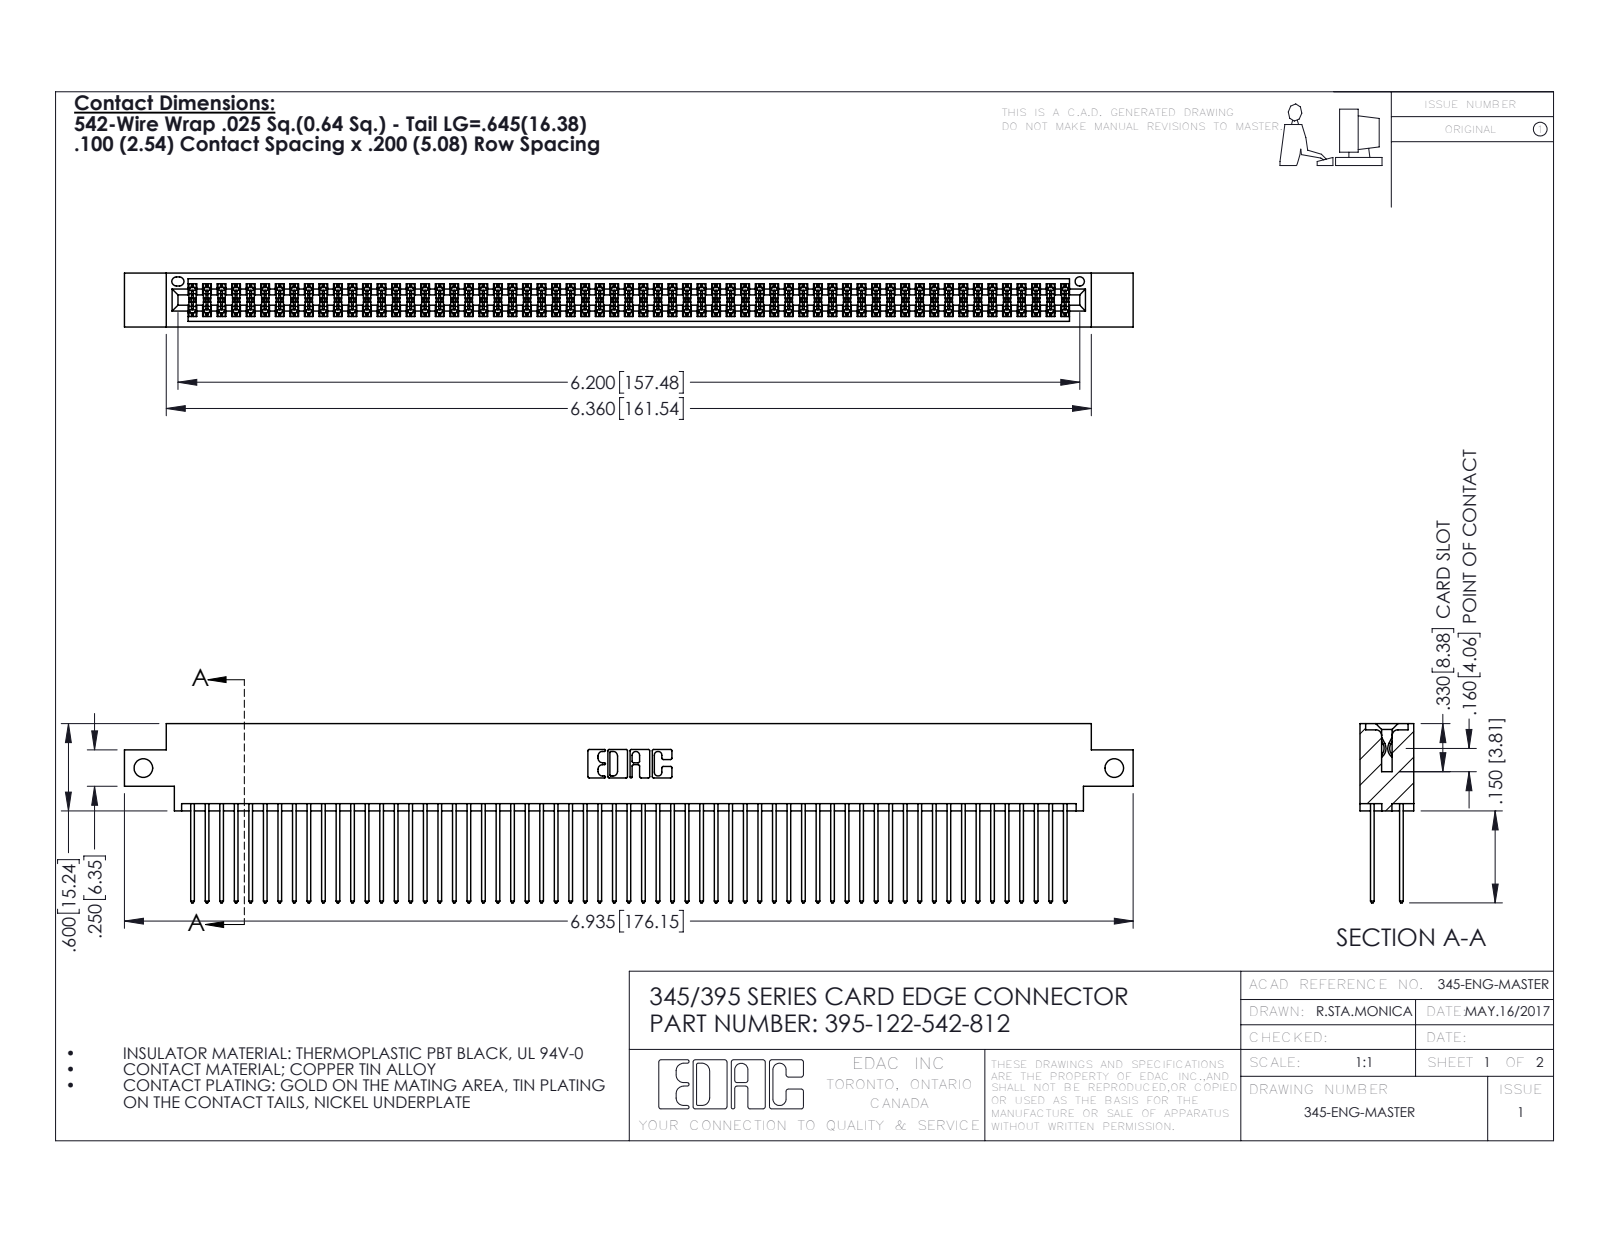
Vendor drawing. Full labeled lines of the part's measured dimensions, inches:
Part name (STEP PRODUCT): 395-122-542-812; 345-292-001_345-293-142; 345 Part_0.170 Offset - Side Mount
STEP written by: SolidWorks 2016 (CONFIG_CONTROL_DESIGN)
Units: inches
Bodies: 123 solids, 6230 faces (4110 planar, 2120 cylindrical, 0 other)
Overall size (bounding box): 6.935 × 1.232 × 0.37
Volume: 1.077 in³ · Surface area: 45.15 in²
Round holes (diameter × count): ⌀0.128 ×2, ⌀0.064 ×1
Partial cylindrical surfaces — rounded edges, fillets, slot ends (radius × count): R0.006 ×183, R0.01 ×122, R0.01 ×22, R0.007 ×6, R0.031 ×6, R0.026 ×3, R0.014 ×2, R0.019 ×2
Main face-to-face distances: 0.298, 0.072, 0.2, 0.098, 0.272, 0.025, 0.37, 0.225, 0.175, 0.149
Hole centre spacings: 6.675
